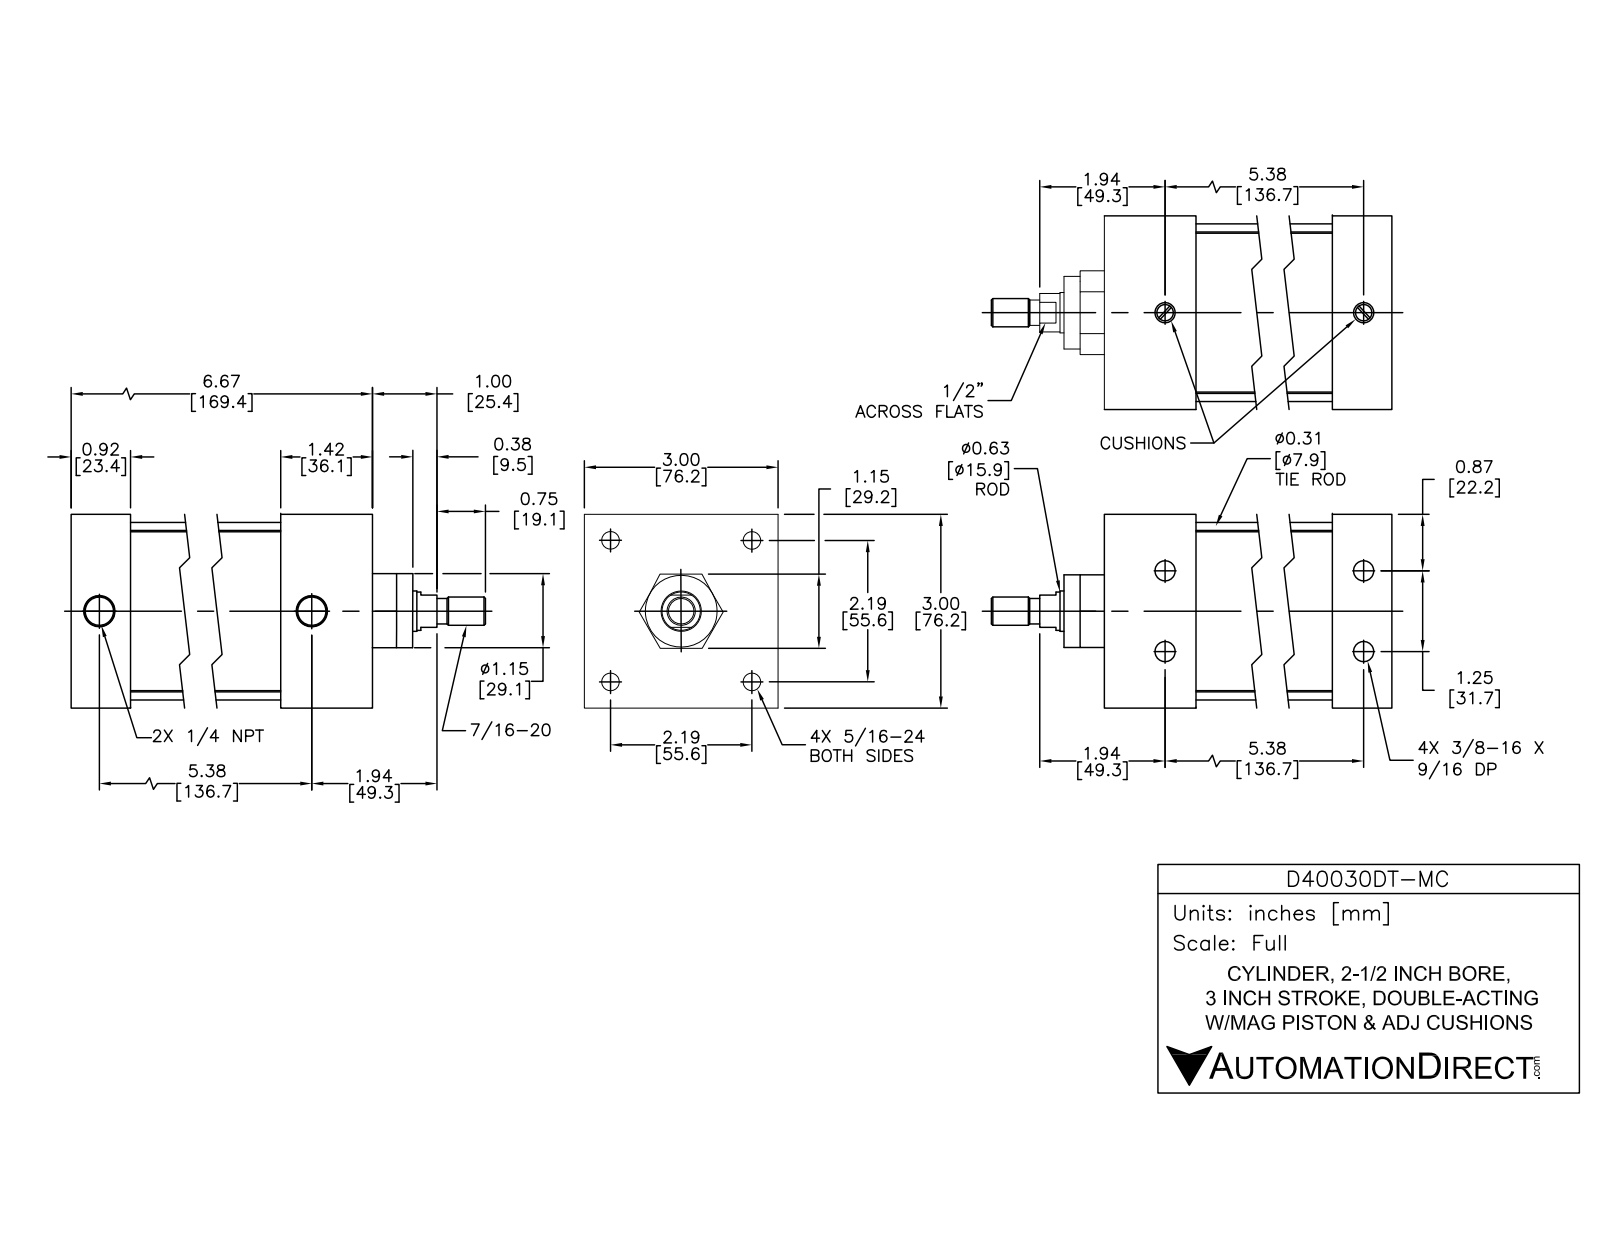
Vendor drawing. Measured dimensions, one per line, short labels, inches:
name: D40030DT-M BODY; D40030DT-MC; D40030DT-M PISTON
written by: SolidWorks 2015 (AUTOMOTIVE_DESIGN)
unit: in
bodies: 12 solids, 298 faces (94 planar, 114 cylindrical, 90 other)
size: 8.496 × 3 × 3
volume: 33.97 in³; area: 218.7 in²
holes: 4× ⌀0.267, 4× ⌀0.307, 4× ⌀0.359, 4× ⌀0.5, 2× ⌀0.297, 2× ⌀0.477, 1× ⌀0.625, 1× ⌀0.628, 1× ⌀2.5
bosses: 4× ⌀0.484, 4× ⌀0.313, 4× ⌀0.282, 1× ⌀2.75, 1× ⌀2.497, 1× ⌀1.12, 1× ⌀0.622, 1× ⌀0.59
rounds: 4× R0.3
face distances: 3, 0.08, 4.326, 6.746, 5.726, 1.02, 1.42, 4.306, 5.326, 1
hole spacings: 1.556, 2.2, 5.406, 5.37, 0.625, 0.625, 1.25, 3.111
